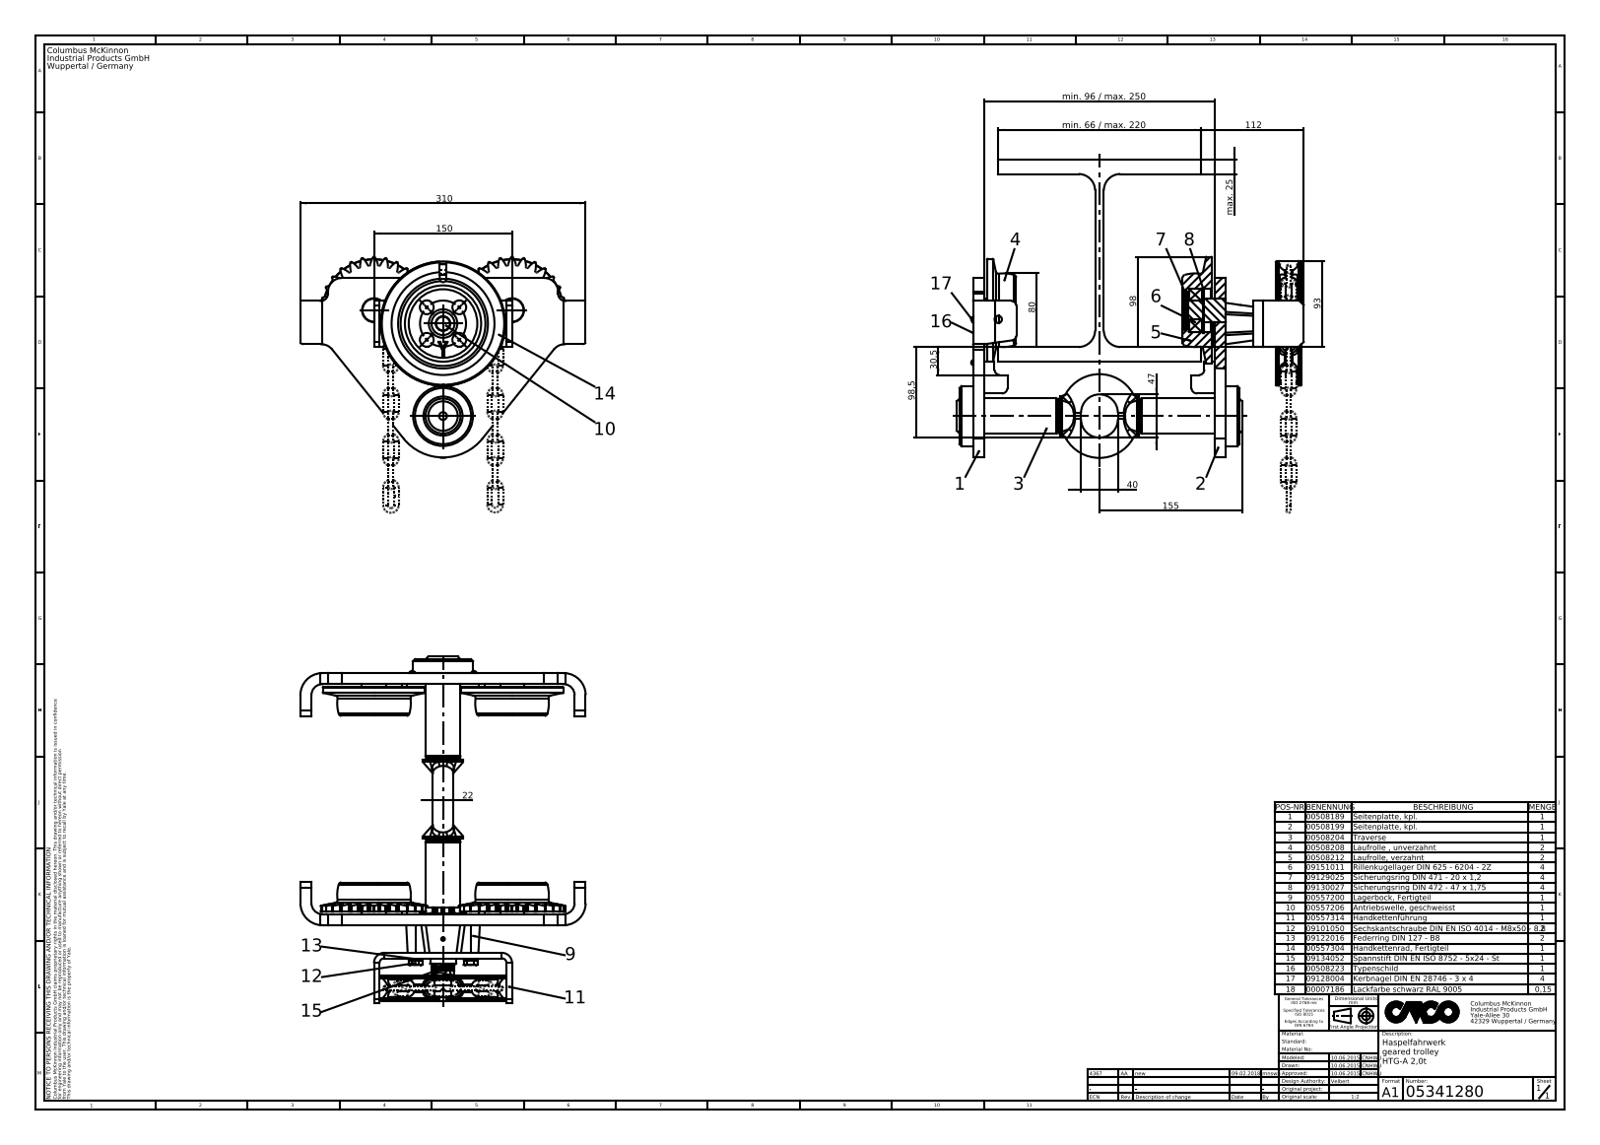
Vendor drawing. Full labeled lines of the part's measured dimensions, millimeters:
Part name (STEP PRODUCT): HTG-A 2,0t
STEP written by: SolidWorks 2015 (AUTOMOTIVE_DESIGN)
Units: millimetres
Bodies: 68 solids, 2111 faces (442 planar, 1004 cylindrical, 665 other)
Overall size (bounding box): 500 × 384.19 × 377
Volume: 6 967 000 mm³ · Surface area: 1 234 000 mm²
Round holes (diameter × count): ⌀2 ×10, ⌀2.5 ×8, ⌀3 ×5, ⌀3.5 ×4, ⌀15 ×4, ⌀9 ×3, ⌀6.8 ×2, ⌀8.1 ×2, ⌀19 ×2, ⌀26 ×2, ⌀36.71 ×2, ⌀38 ×2
Round bosses / shafts (diameter × count): ⌀5 ×22, ⌀5.2 ×4, ⌀111 ×2, ⌀49.5 ×2, ⌀26.99 ×2, ⌀20 ×2, ⌀14.1 ×2, ⌀8 ×2
Partial cylindrical surfaces — rounded edges, fillets, slot ends (radius × count): R1 ×134, R20 ×112, R1.5 ×56, R10 ×22, R2 ×8, R2.5 ×8, R6 ×8, R11 ×4
Main face-to-face distances: 16, 204, 220, 12, 188, 132.25, 141.75, 9.5, 262, 120.25
Hole centre spacings: 21.55, 11.49, 150, 50.85, 5, 10.13, 11.57, 16.24
